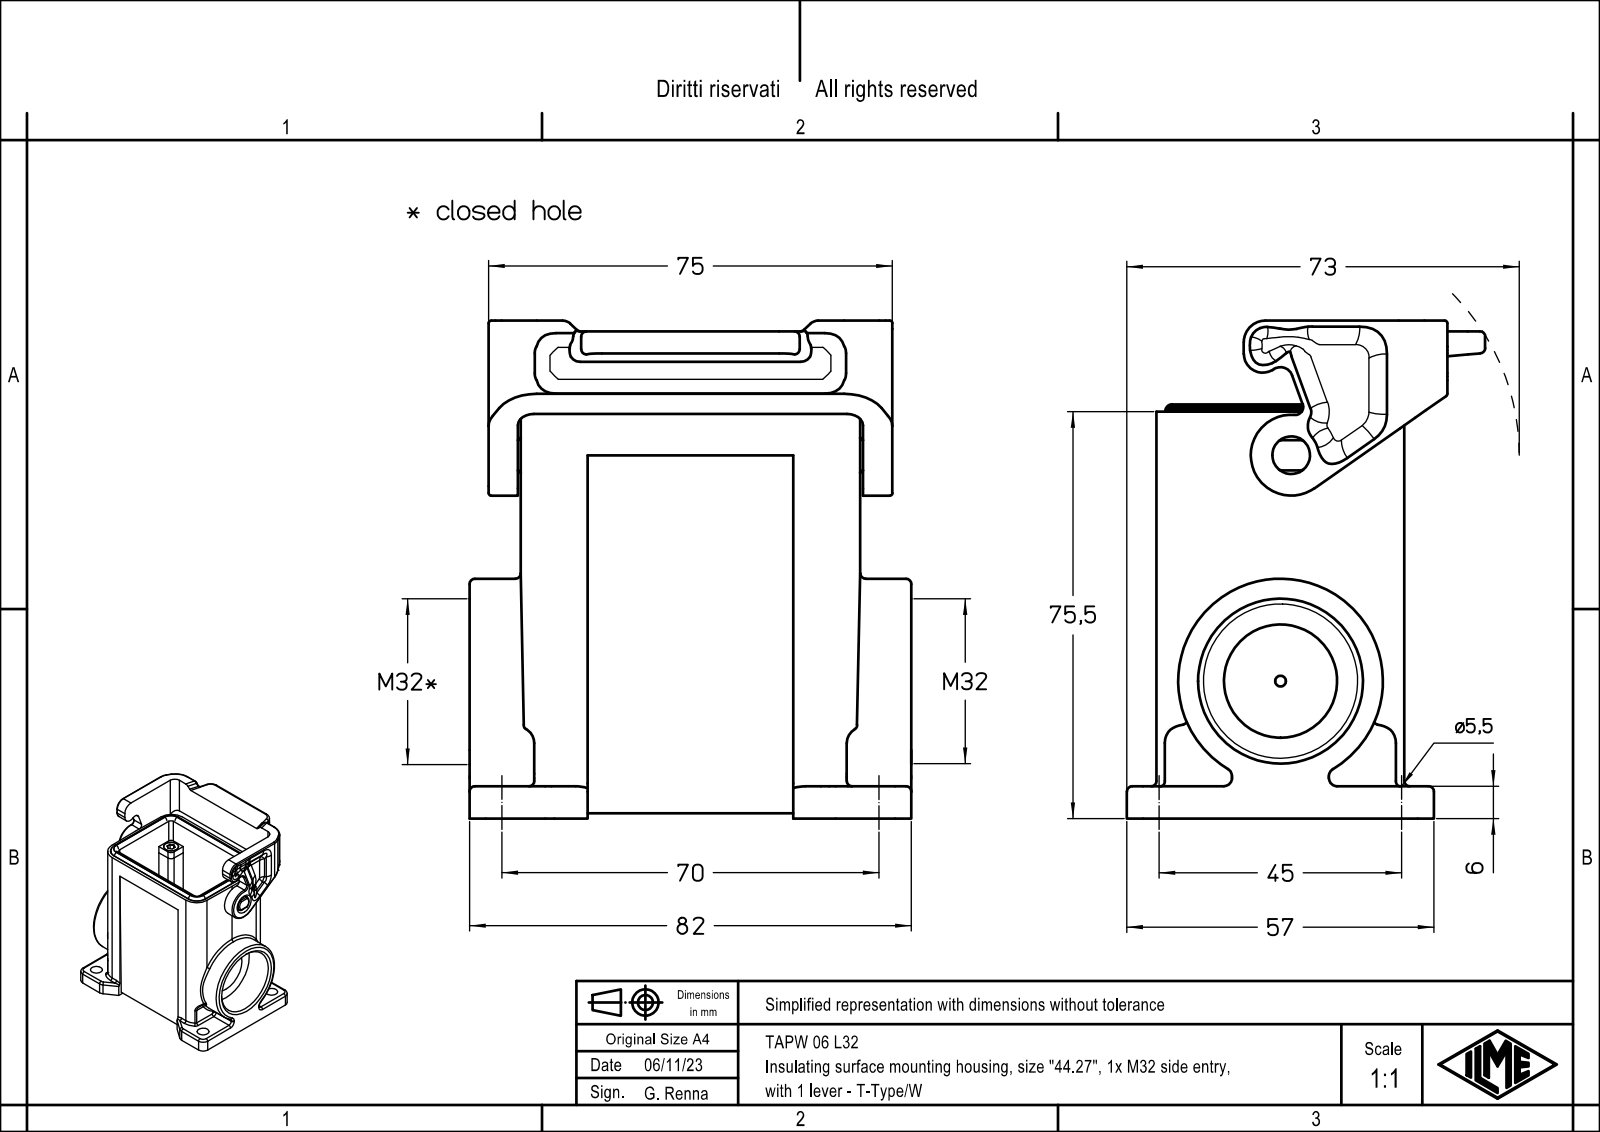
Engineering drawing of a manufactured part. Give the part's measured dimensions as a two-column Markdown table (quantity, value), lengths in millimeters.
| quantity | value |
| --- | --- |
| part name | TAPW 06 L32 |
| STEP written by | Creo Elements/Direct Modeling 20.1B 02-Apr-2019 (C) Parametric Technology GmbH (AUTOMOTIVE_DESIGN) |
| units | millimeters |
| bodies | 1 solid, 326 faces (162 planar, 128 cylindrical, 36 other) |
| overall size | 92.4 × 82 × 66.5 |
| volume | 125 546 mm³ |
| surface area | 47 943 mm² |
| round holes (diameter × count) | 5.5 × 4, 28 × 1, 30.6 × 1 |
| round bosses / shafts (diameter × count) | 38 × 1 |
| partial cylindrical surfaces (radius × count) | 3 × 17, 2 × 10, 1.5 × 9, 1 × 8, 1.3 × 8, 0.5 × 4, 6 × 4, 7 × 4 |
| main face-to-face distances | 5.4, 40.6, 46, 35.2, 5.5, 1, 14.9, 9, 58.1, 5.9 |
| hole center spacings | 45, 70, 83.22 |
